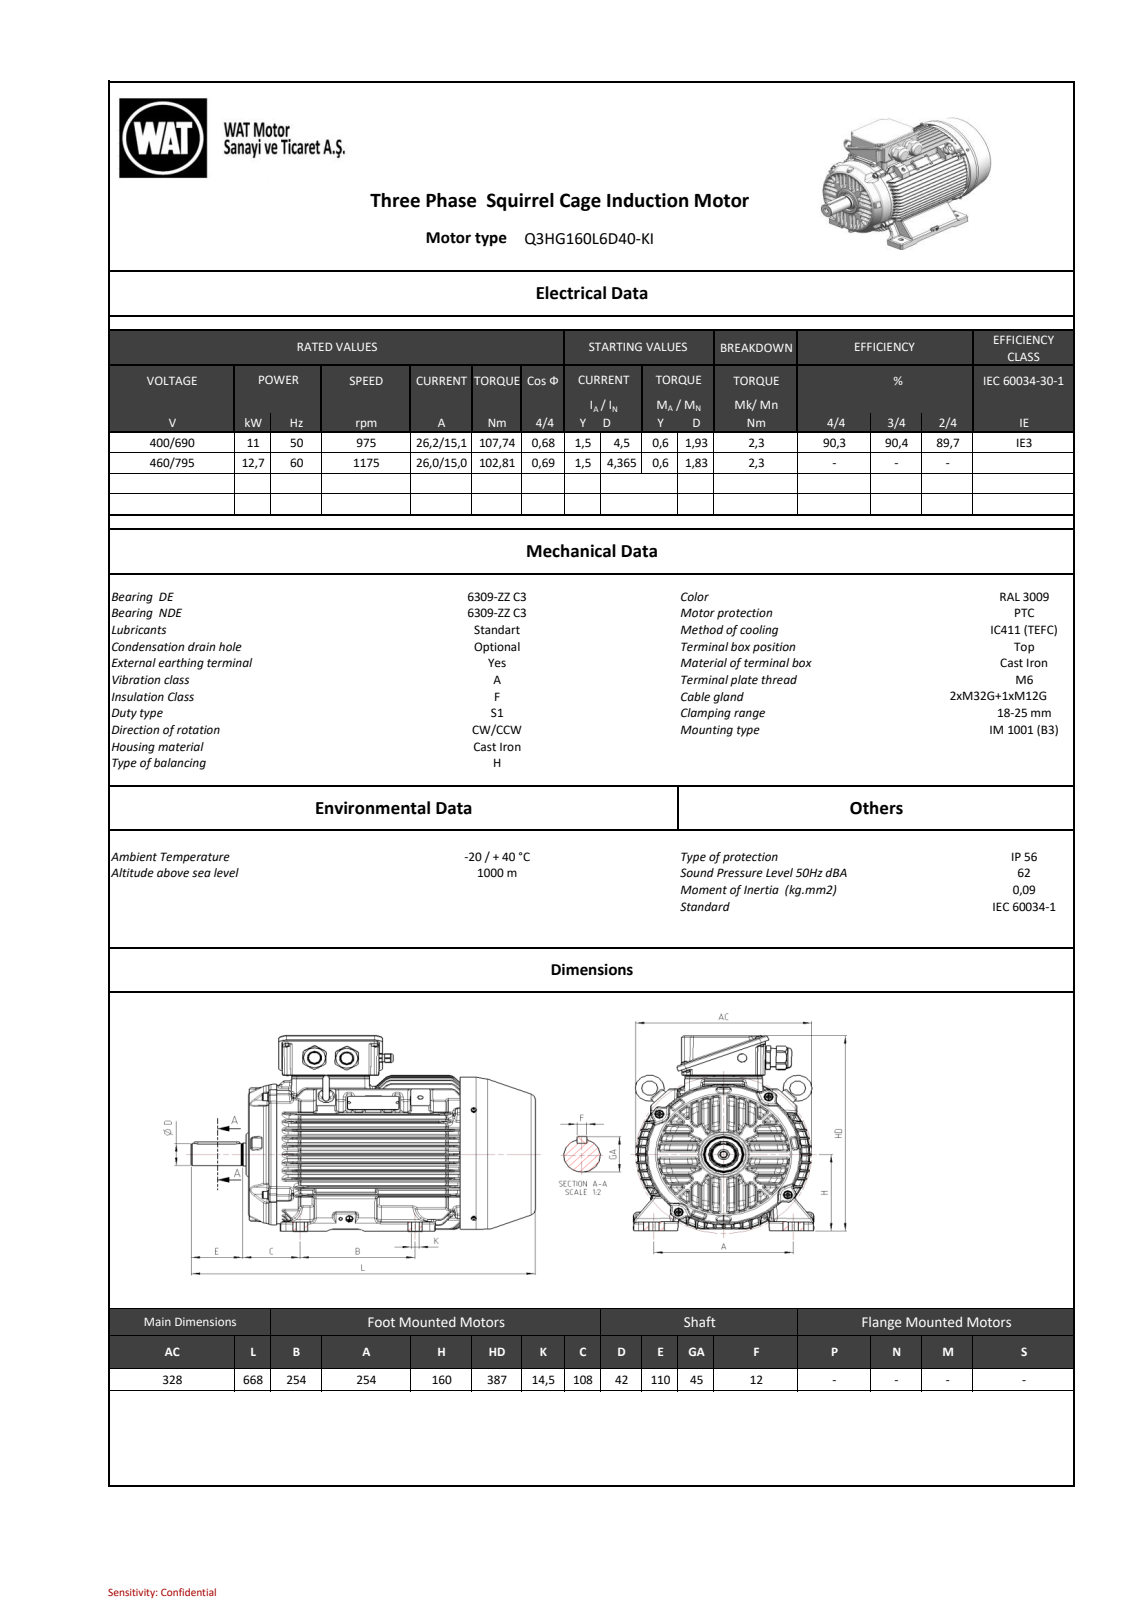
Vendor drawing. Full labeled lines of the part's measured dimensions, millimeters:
Part name (STEP PRODUCT): C9017F38B806sw74
STEP written by: SIEMENS PLM Software NX 11.0 (AUTOMOTIVE_DESIGN)
Units: millimetres
Bodies: 0 solids, 6299 faces (1238 planar, 1844 cylindrical, 3217 other)
Overall size (bounding box): 667.5 × 388.3 × 327.37
Round holes (diameter × count): ⌀5.5 ×8, ⌀9 ×8, ⌀4.2 ×7, ⌀5.3 ×4, ⌀10.9 ×2, ⌀5.2 ×1, ⌀10 ×1, ⌀14 ×1, ⌀17 ×1, ⌀19 ×1, ⌀21 ×1, ⌀24.2 ×1
Round bosses / shafts (diameter × count): ⌀16 ×8, ⌀20 ×4, ⌀30 ×2, ⌀10 ×2, ⌀317 ×1, ⌀282 ×1, ⌀45 ×1, ⌀42 ×1
Partial cylindrical surfaces — rounded edges, fillets, slot ends (radius × count): R5 ×243, R3 ×202, R4 ×144, R1.5 ×112, R2 ×64, R1.8 ×58, R0.4 ×37, R6 ×31
Main face-to-face distances: 137.45, 15.17, 30.42, 122.2, 15.25, 45.73, 106.89, 30.56, 15.31, 107.03
Hole centre spacings: 136, 144, 203.65, 123.22, 183.51, 183.52, 123.21, 50.01
